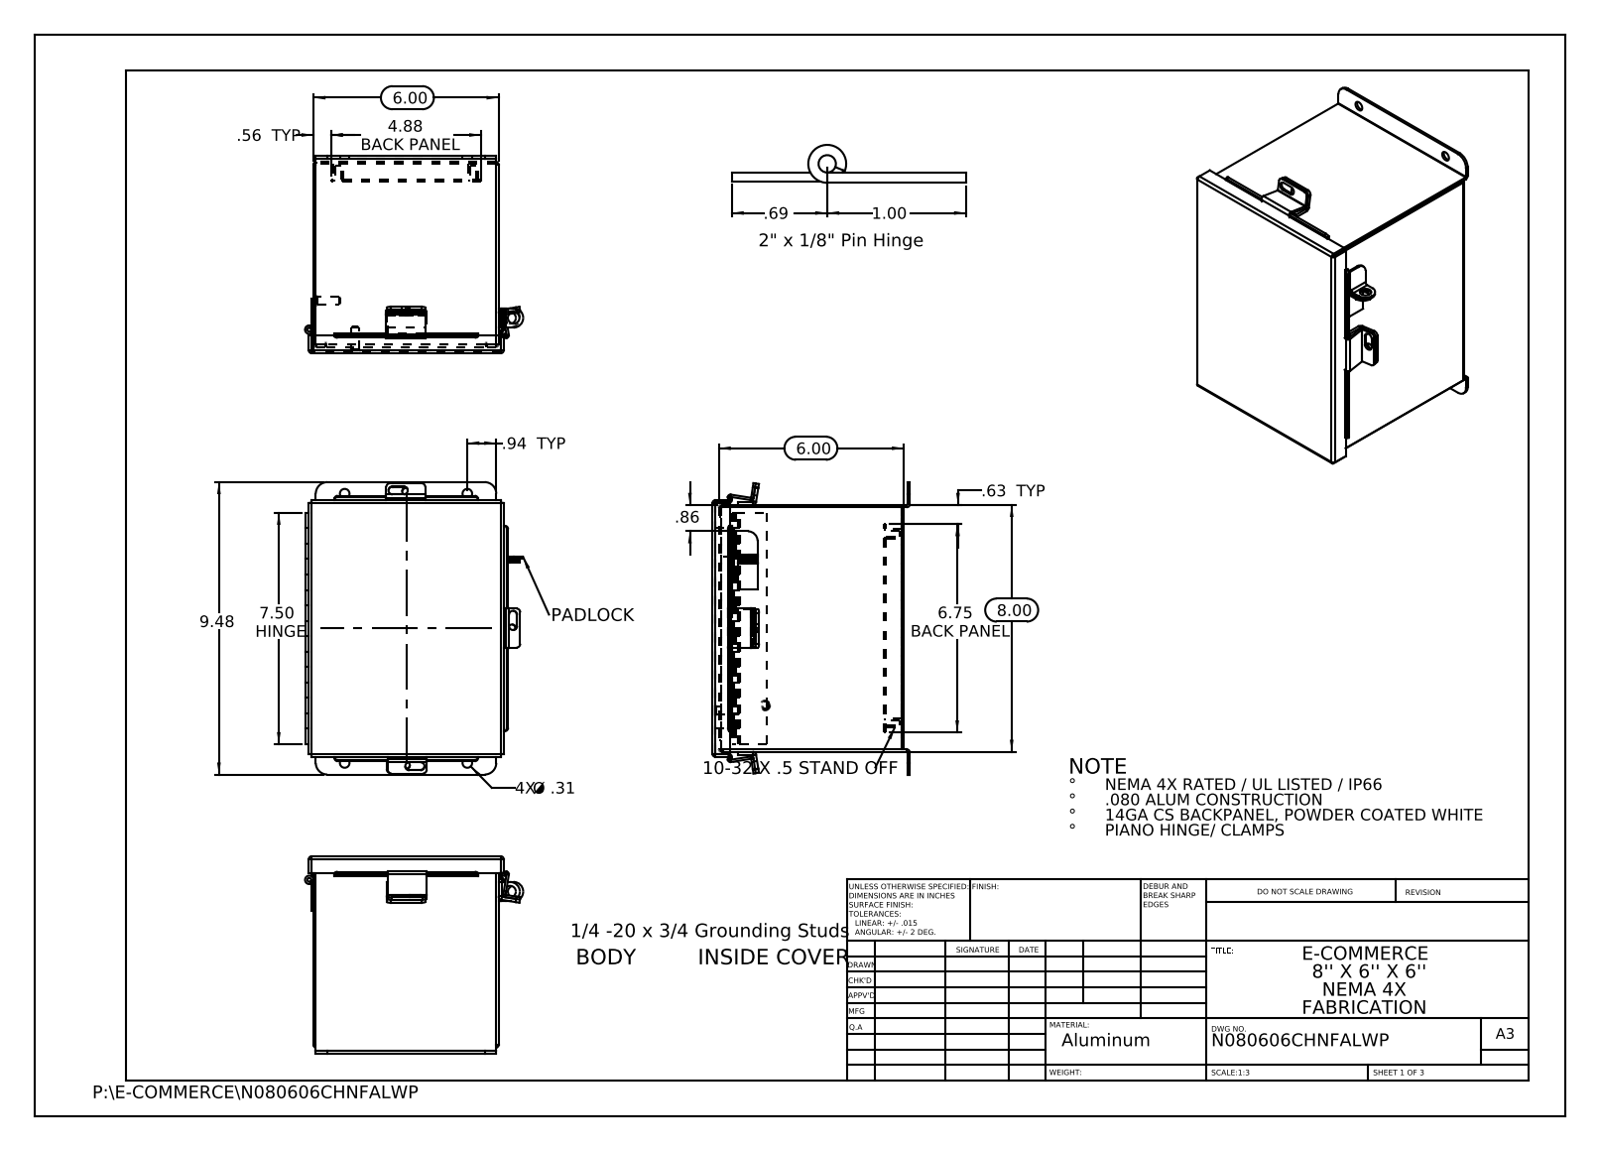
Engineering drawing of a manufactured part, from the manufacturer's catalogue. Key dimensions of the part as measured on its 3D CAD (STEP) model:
Part name (STEP PRODUCT): N080606CHNFALWP JIC Top; HW-CLH-JH-20104; N080606CHNFALWP Hinge Body Side; N080606CHNFALWP JIC_Standoff (+8 more)
STEP written by: SolidWorks 2013 (CONFIG_CONTROL_DESIGN)
Units: inches
Bodies: 21 solids, 584 faces (363 planar, 201 cylindrical, 20 other)
Overall size (bounding box): 9.476 × 7.072 × 6.39
Volume: 26.69 in³ · Surface area: 734.7 in²
Round holes (diameter × count): ⌀0.25 ×7, ⌀0.187 ×4, ⌀0.312 ×4, ⌀0.125 ×1, ⌀0.125 ×1, ⌀0.373 ×1, ⌀0.375 ×1
Round bosses / shafts (diameter × count): ⌀0.313 ×4, ⌀0.315 ×2, ⌀0.236 ×2, ⌀0.273 ×1, ⌀0.25 ×1
Partial cylindrical surfaces — rounded edges, fillets, slot ends (radius × count): R0.013 ×13, R0.009 ×12, R0.088 ×12, R0.125 ×10, R0.083 ×6, R0.1 ×6, R0.133 ×6, R0.375 ×4
Main face-to-face distances: 0.075, 5.925, 6.128, 7.925, 6, 5.85, 6.053, 6.203, 7.85, 8
Hole centre spacings: 1.315, 4.373, 7.429, 8.519, 3.976, 4.375, 6.126, 7.528
